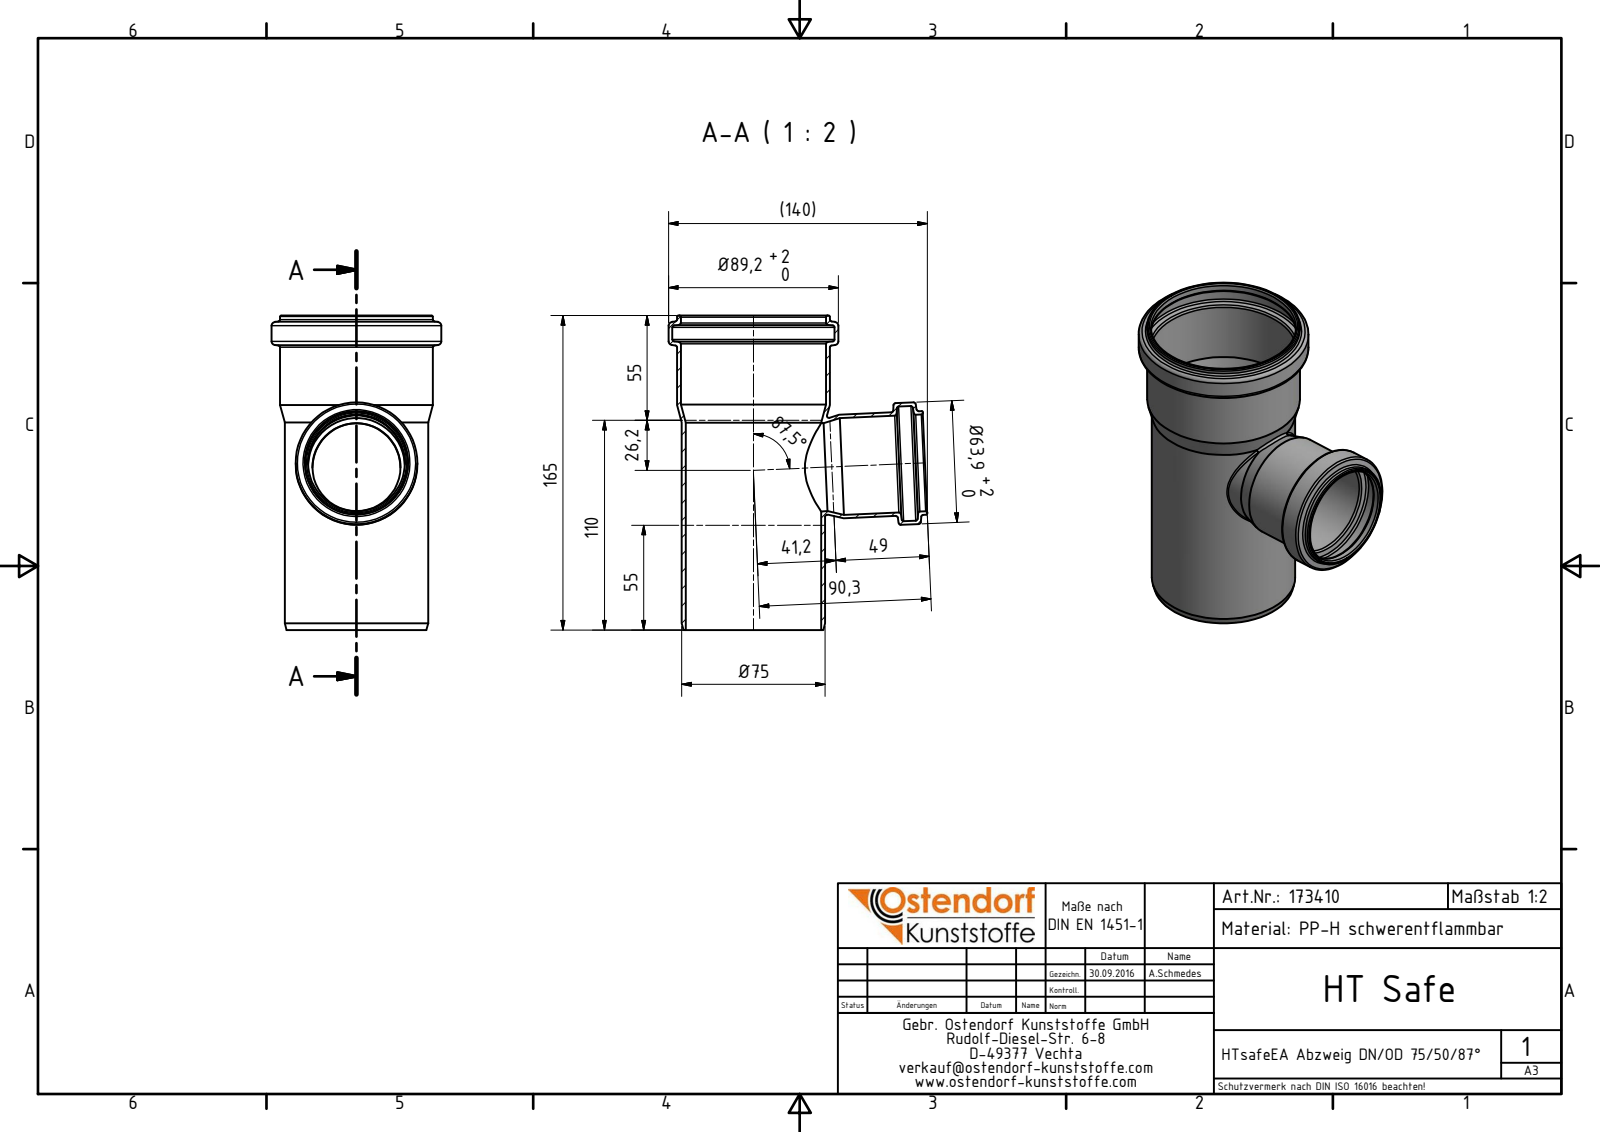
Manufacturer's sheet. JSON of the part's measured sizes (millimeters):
{"part_name": "173410 HTsafeEA DN_OD 75_50_87°", "step_written_by": "Autodesk Inventor 2016 (AUTOMOTIVE_DESIGN)", "units": "millimeters", "bodies": {"solids": 1, "faces": 54, "planar": 3, "cylindrical": 16, "other": 35}, "overall_size": [165, 135.88, 89.2], "volume_mm3": 100658, "surface_area_mm2": 100640, "round_holes": [[50.8, 2], [46.2, 1], [60.3, 1], [71.1, 1], [76.2, 1], [85.2, 1]], "round_bosses_or_shafts": [[54.4, 2], [89.2, 1], [80.2, 1], [75.3, 1], [63.9, 1], [50, 1]], "face_to_face_distances": [165]}
